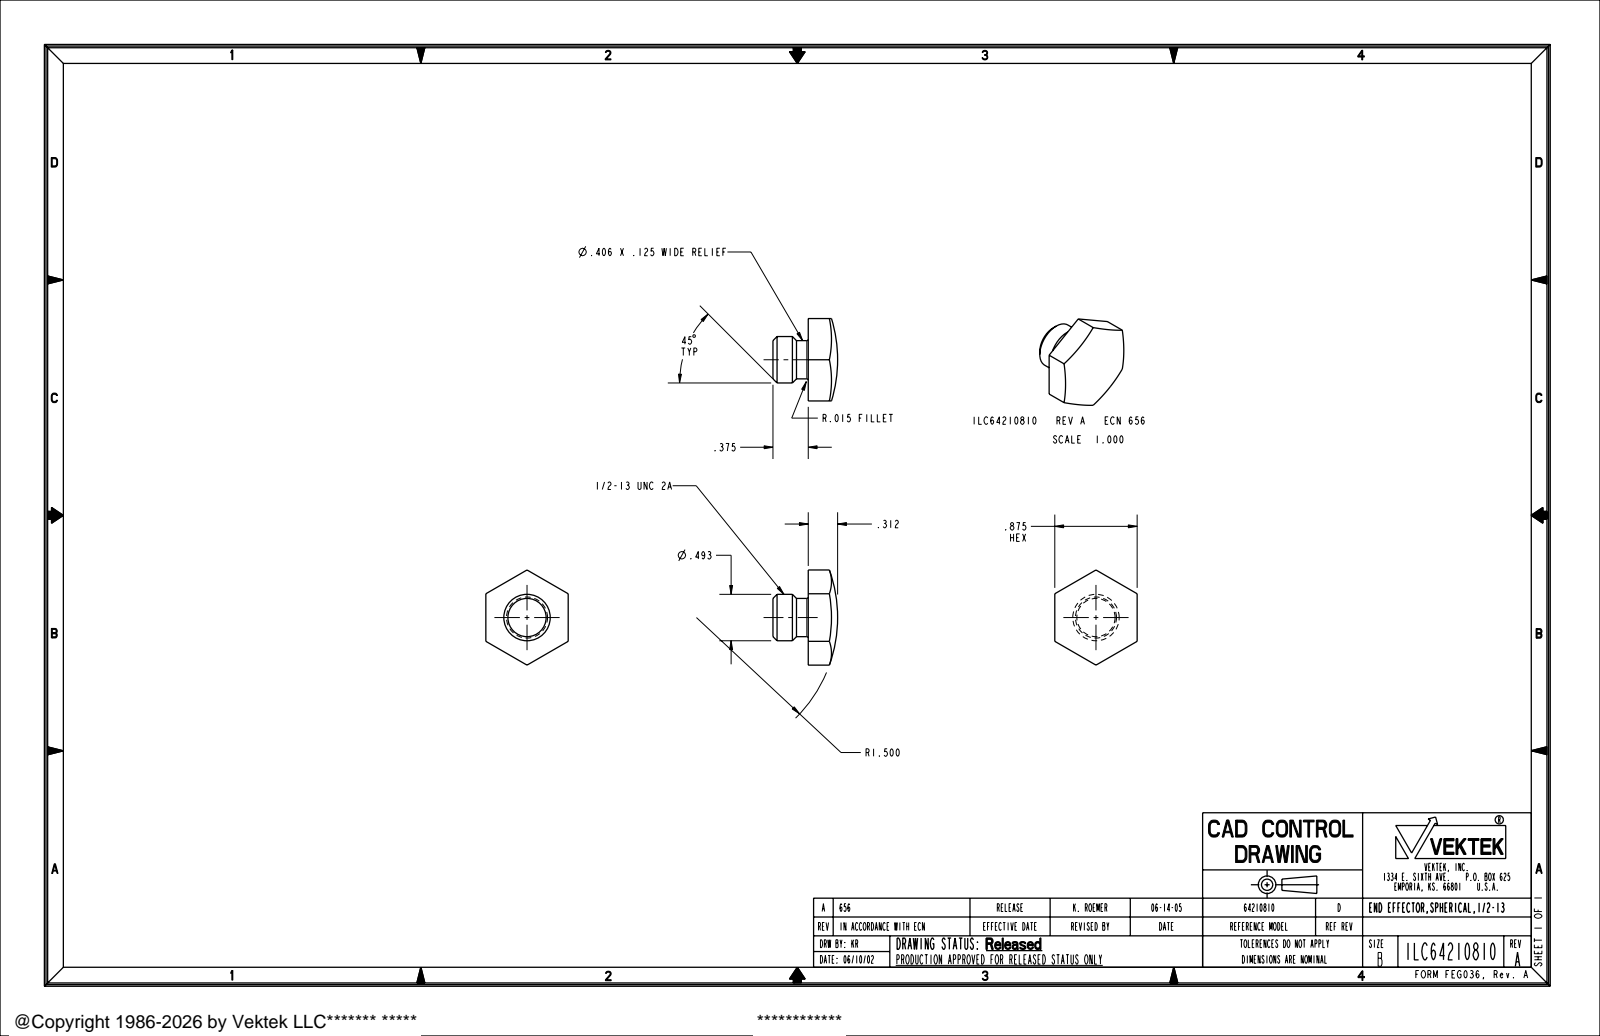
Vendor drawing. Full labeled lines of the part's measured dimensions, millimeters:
Part name (STEP PRODUCT): ILC64210810
STEP written by: PRO/ENGINEER BY PARAMETRIC TECHNOLOGY CORPORATION, 2004290 (AUTOMOTIVE_DESIGN_CC2)
Units: millimetres
Bodies: 1 solid, 20 faces (8 planar, 4 cylindrical, 8 other)
Overall size (bounding box): 25.7 × 22.2 × 17.4
Volume: 4 000 mm³ · Surface area: 1 707 mm²
Round bosses / shafts (diameter × count): ⌀12.5 ×1, ⌀10.3 ×1
Main face-to-face distances: 22.2, 9.5
